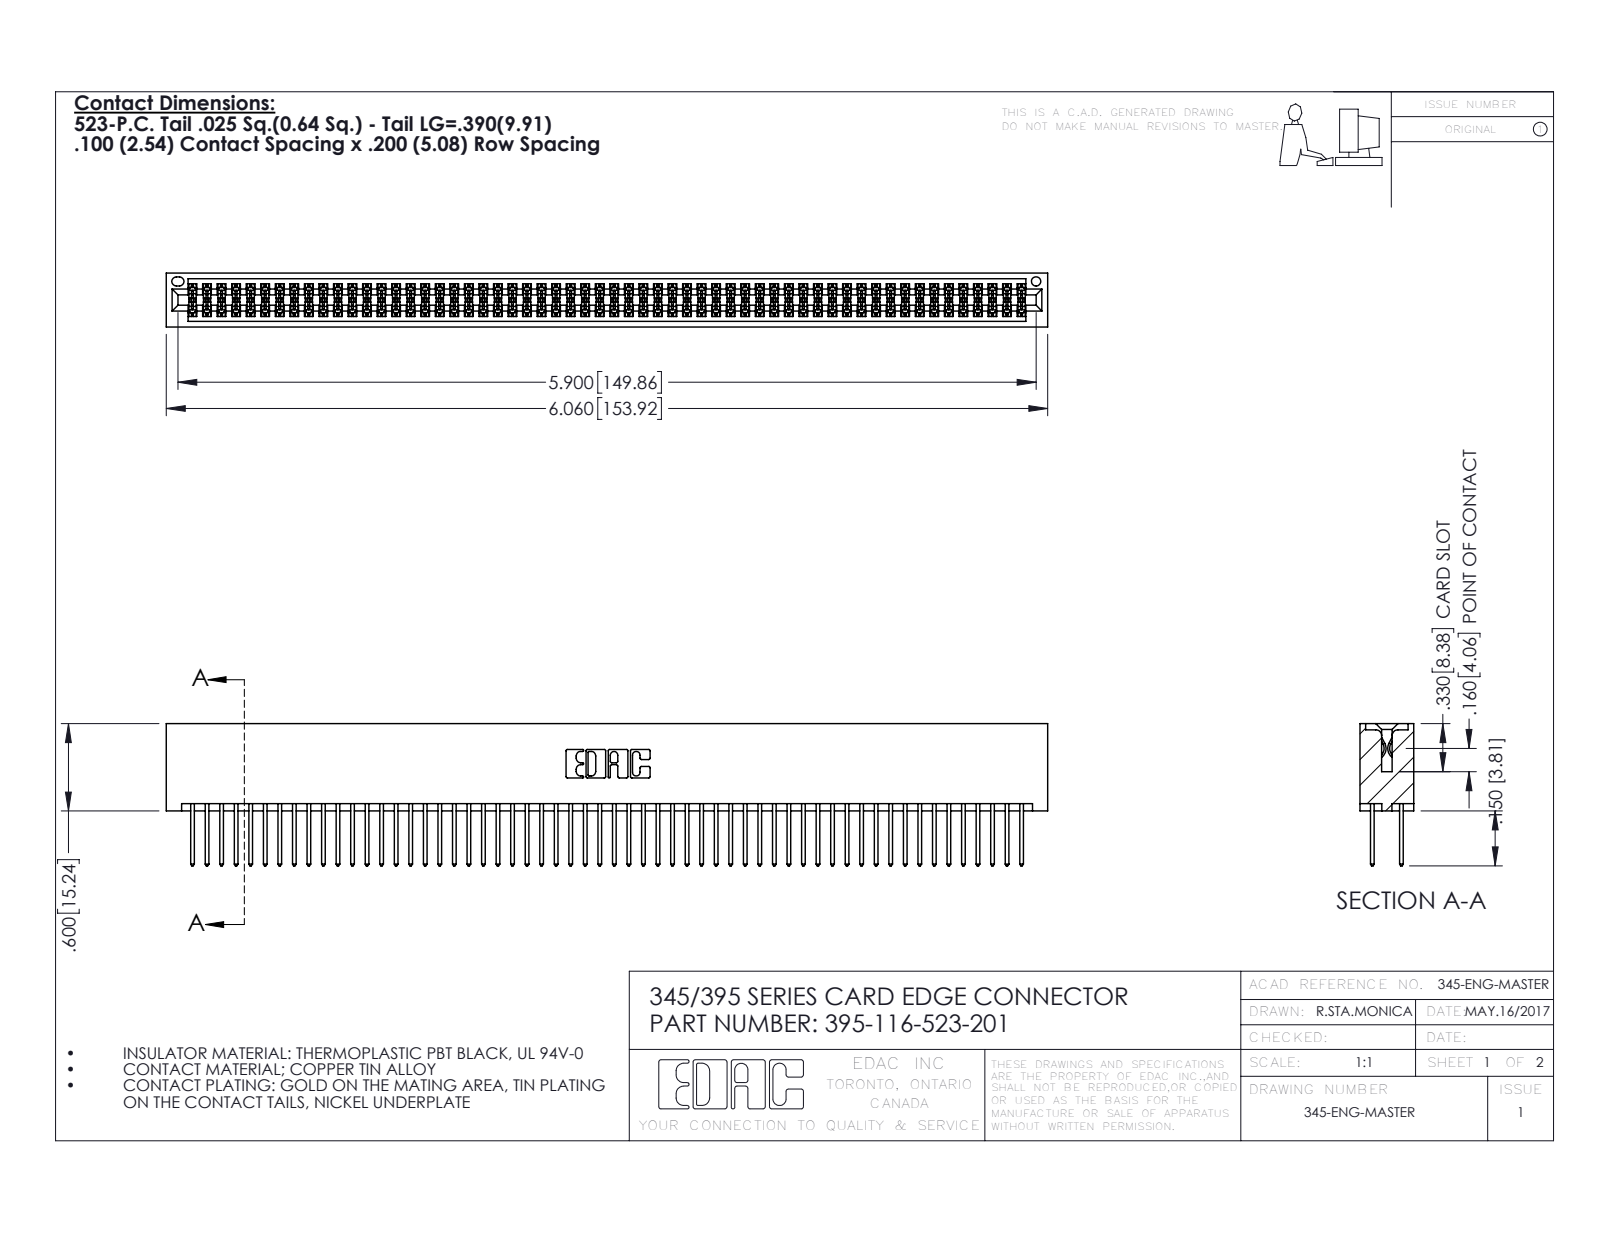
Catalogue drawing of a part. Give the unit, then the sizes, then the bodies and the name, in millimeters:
Units: millimetres
Overall size (bounding box): 153.9 × 24.8 × 9.4
Round holes (diameter × count): ⌀1.6 ×1
Partial cylindrical surfaces — rounded edges, fillets, slot ends (radius × count): R0.2 ×174, R0.3 ×116, R0.3 ×22, R0.2 ×6, R0.8 ×6, R0.7 ×3, R0.4 ×2, R0.5 ×2
Main face-to-face distances: 7.6, 1.8, 5.1, 2.5, 6.9, 0.6, 9.4, 5.7, 4.4, 3.8
Volume: 16 000 mm³ · Surface area: 25 260 mm²
Bodies: 117 solids, 5918 faces (3904 planar, 2014 cylindrical, 0 other)
Part name (STEP PRODUCT): 345-292-001_345-293-123; 345 Part_No Mounting Lugs; 395-116-523-201
STEP written by: SolidWorks 2016 (CONFIG_CONTROL_DESIGN)
